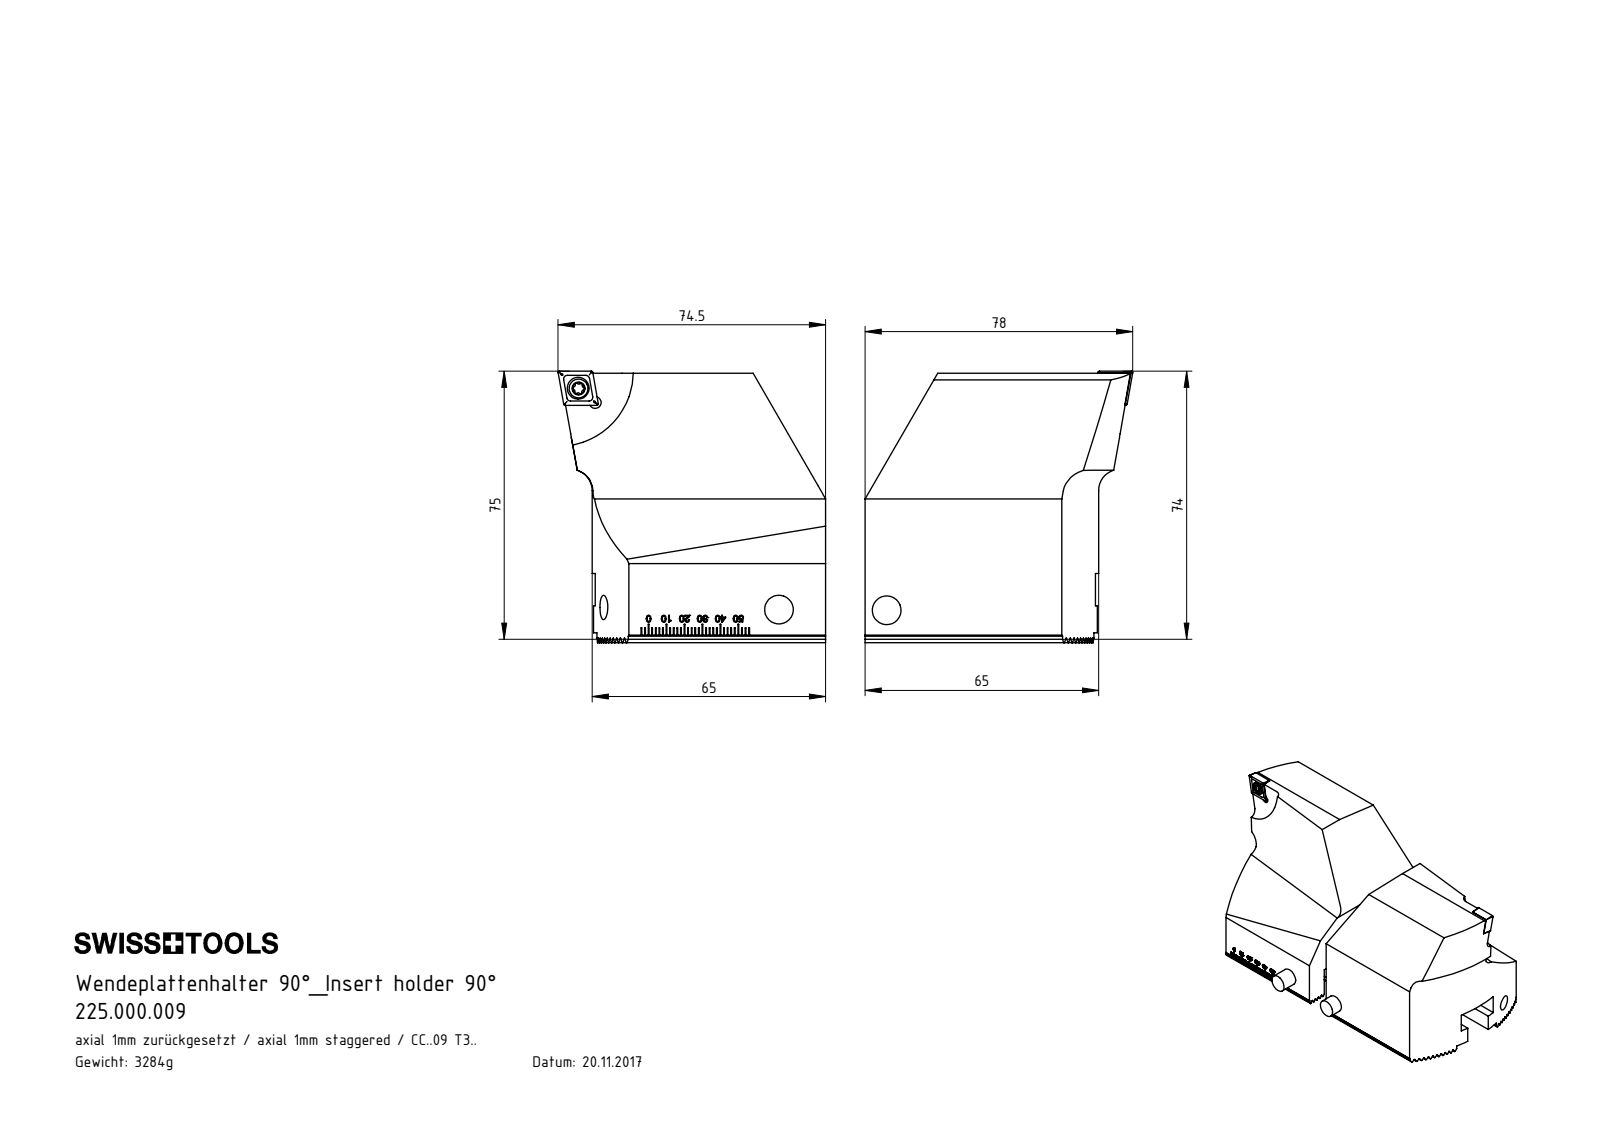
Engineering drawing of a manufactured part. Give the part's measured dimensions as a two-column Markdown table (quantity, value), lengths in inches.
| quantity | value |
| --- | --- |
| part name | ISO 8734 - 8 x 20 m6; ISO 8734 - 8 x 24 m6; ISO 4028 - M8 x 35; 225.000.009 (+3 more) |
| STEP written by | SolidWorks 2017 (CONFIG_CONTROL_DESIGN) |
| units | inches |
| bodies | 12 solids, 1132 faces (686 planar, 140 cylindrical, 306 other) |
| overall size | 6.299 × 3.449 × 2.975 |
| volume | 25.65 in³ |
| surface area | 99.95 in² |
| round holes (diameter × count) | 0.13 × 4, 0.315 × 4, 0.173 × 2, 0.24 × 2, 0.268 × 2 |
| round bosses / shafts (diameter × count) | 0.315 × 2, 0.217 × 2, 0.207 × 2, 0.157 × 2 |
| partial cylindrical surfaces (radius × count) | 0.006 × 22, 0.013 × 12, 0.023 × 12, 0.157 × 2, 0.207 × 2, 0.827 × 2, 2.559 × 2, 2.717 × 2 |
| main face-to-face distances | 0.068, 0.341, 0.136, 2.756, 0.273, 0.205, 1.705, 0.965, 1.791, 0.409 |
| hole center spacings | 0.239, 0.244, 0.276, 1.181, 3.034, 3.229, 3.27, 3.275 |
